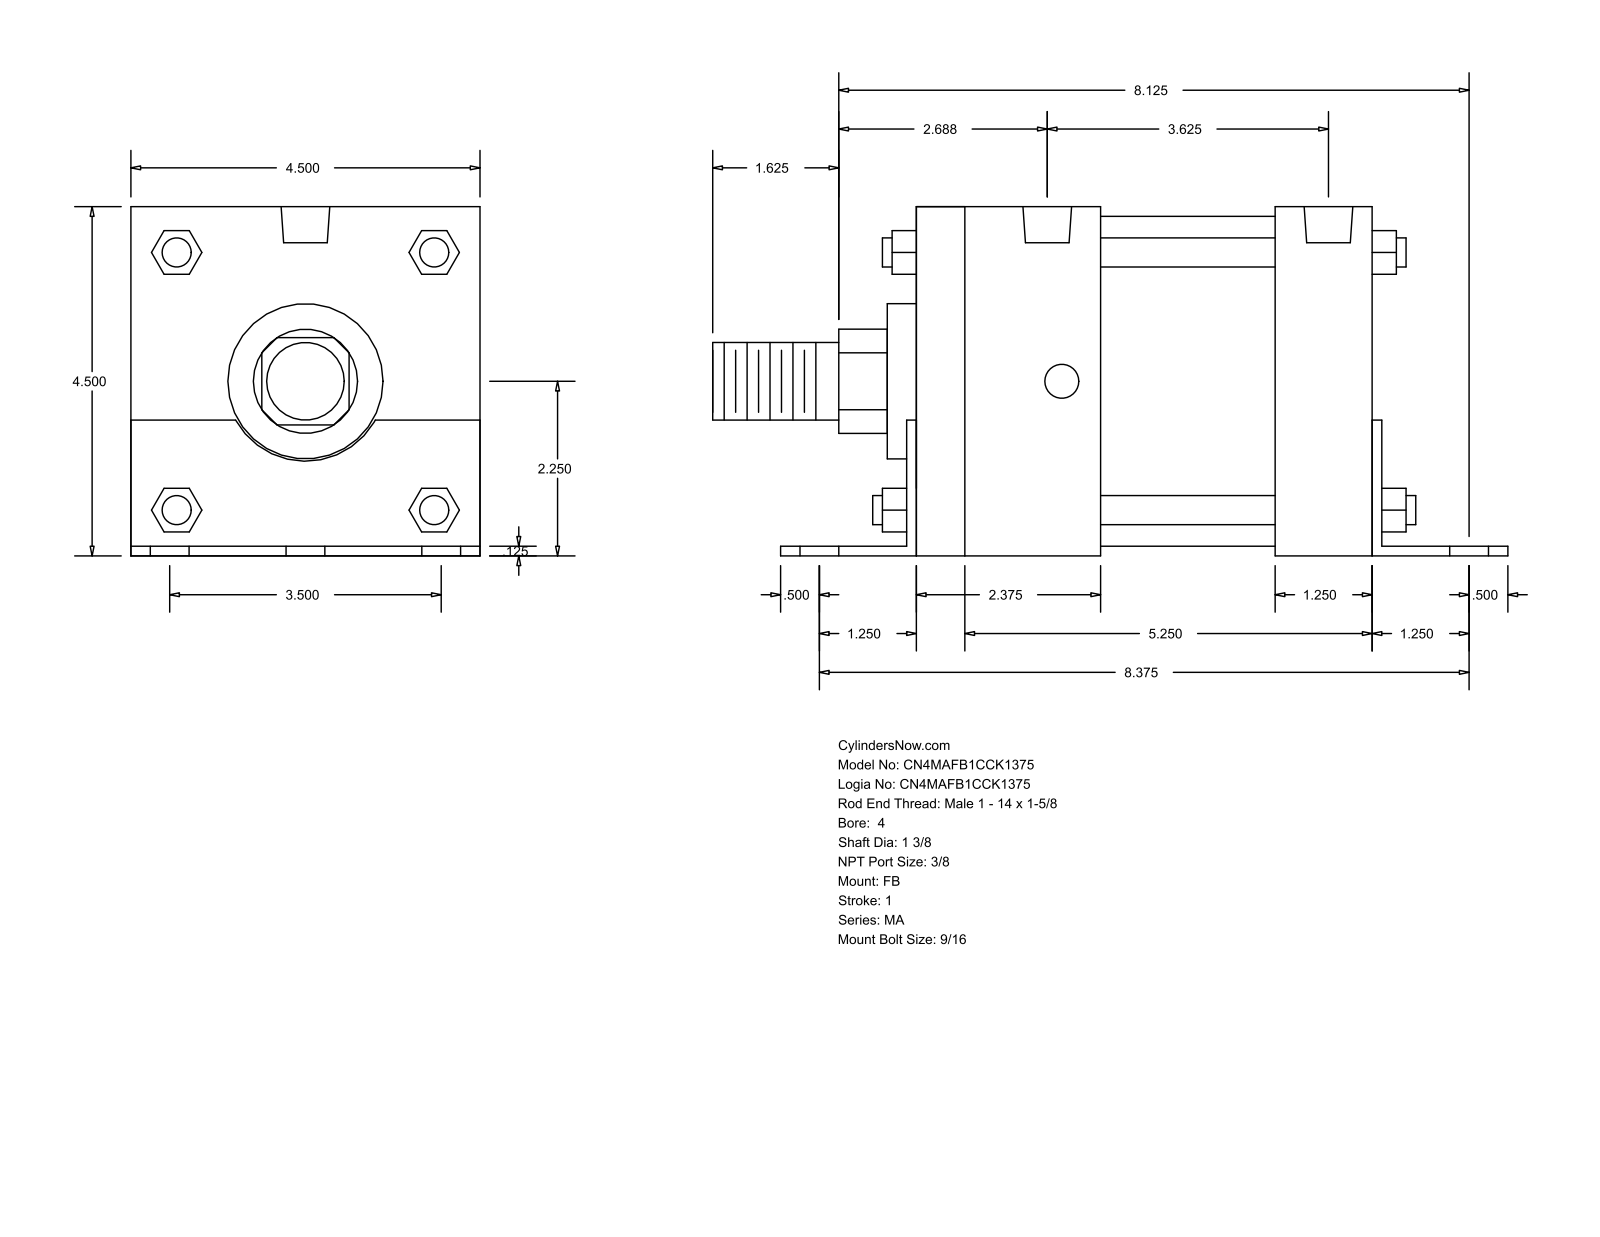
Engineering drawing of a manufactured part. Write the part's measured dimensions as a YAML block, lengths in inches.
part_name: "MA_FB__0400_1.375"
step_written_by: "GSSL Pune (CONFIG_CONTROL_DESIGN)"
units: inches
bodies: {solids: 0, faces: 140, planar: 105, cylindrical: 35, other: 0}
overall_size: [10.25, 4.502, 4.5]
round_holes:
  - {diameter: 0.563, count: 6}
  - {diameter: 0.437, count: 4}
  - {diameter: 0.627, count: 2}
round_bosses_or_shafts:
  - {diameter: 0.375, count: 4}
  - {diameter: 4.25, count: 1}
  - {diameter: 2, count: 1}
  - {diameter: 1.375, count: 1}
  - {diameter: 1, count: 1}
partial_cylinders:
  - {radius: 0.672, count: 1}
  - {radius: 1.03, count: 1}
face_to_face_distances: [4.5, 0.125, 4.502, 0.123, 4.377, 5.875, 0.125, 6, 6, 6.125]
hole_center_spacings: [1.75, 8.556, 8.375, 0.188, 2.52, 2.658, 3.25, 3.419]
